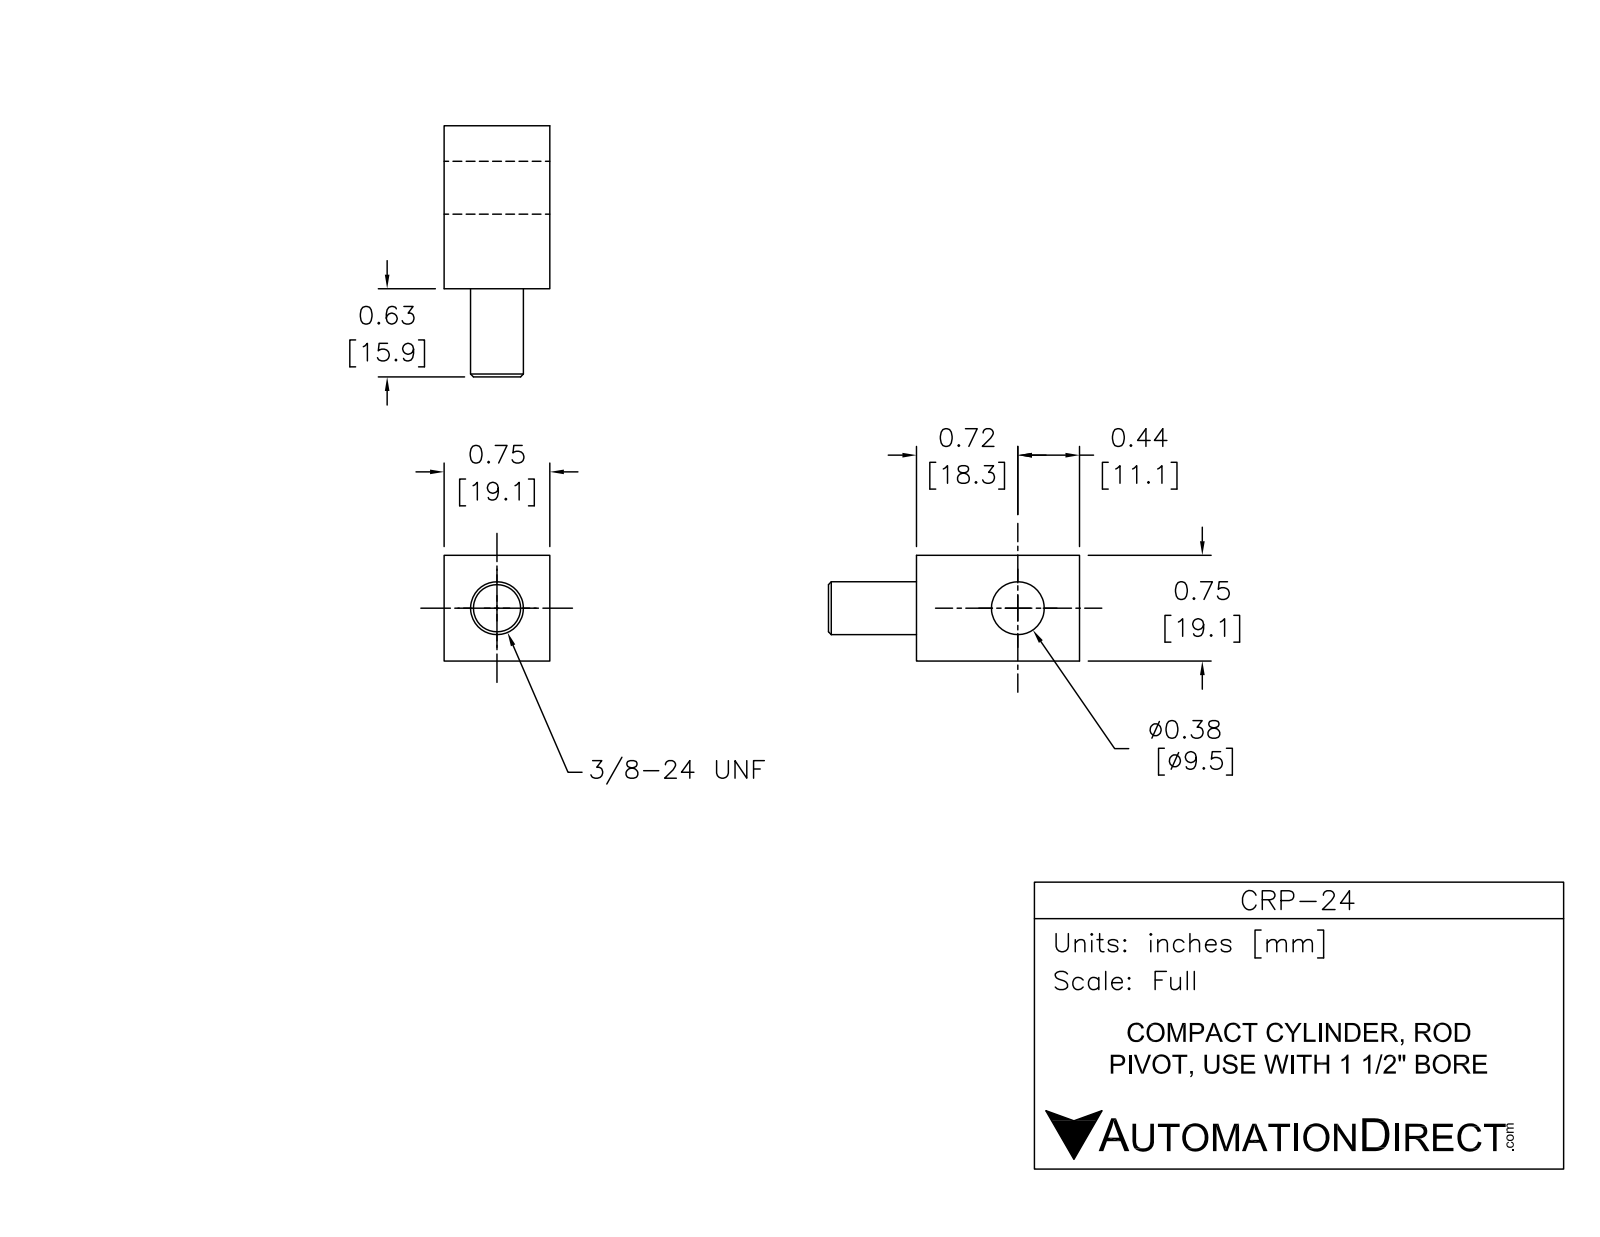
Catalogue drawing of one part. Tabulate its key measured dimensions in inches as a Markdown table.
| quantity | value |
| --- | --- |
| part name | CRP-24_nut; CRP-24_bushing; CRP-24_rr; CRP-24 |
| STEP written by | SolidWorks 2014 (AUTOMOTIVE_DESIGN) |
| units | inches |
| bodies | 3 solids, 45 faces (17 planar, 10 cylindrical, 18 other) |
| overall size | 1.79 × 0.75 × 0.75 |
| volume | 0.676 in³ |
| surface area | 9.332 in² |
| round holes (diameter × count) | 0.33 × 1, 0.38 × 1, 0.5 × 1 |
| round bosses / shafts (diameter × count) | 0.375 × 1 |
| main face-to-face distances | 0.75, 1.16, 0.56, 0.095, 0.655, 0.22, 1.38, 0.41, 0.63, 1.79 |
